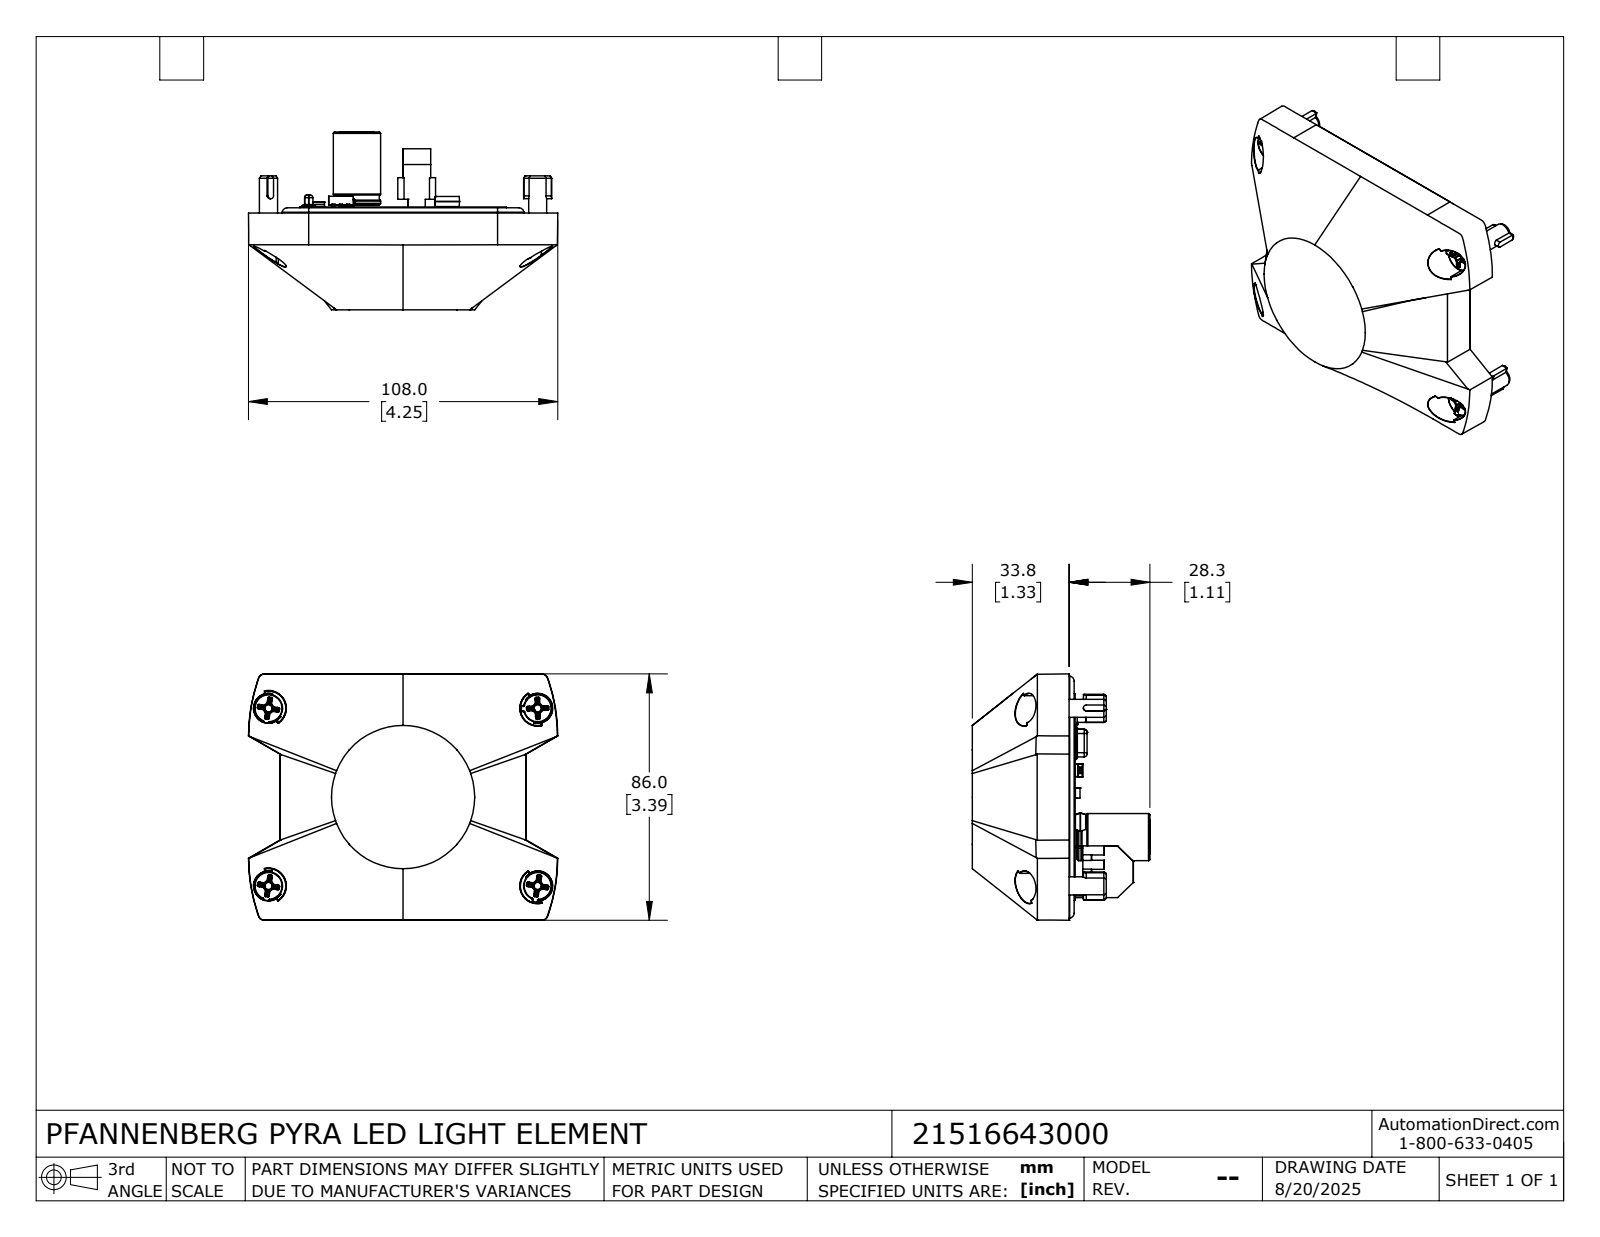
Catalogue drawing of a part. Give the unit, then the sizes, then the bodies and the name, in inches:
Units: inches
Overall size (bounding box): 4.252 × 3.386 × 2.444
Round holes (diameter × count): ⌀0.039 ×12, ⌀0.031 ×8, ⌀0.043 ×7, ⌀0.035 ×2, ⌀0.055 ×2, ⌀0.059 ×2, ⌀0.098 ×2, ⌀0.118 ×2, ⌀0.04 ×1, ⌀0.097 ×1, ⌀0.137 ×1, ⌀0.162 ×1
Round bosses / shafts (diameter × count): ⌀0.386 ×4, ⌀0.248 ×4, ⌀0.65 ×1
Partial cylindrical surfaces — rounded edges, fillets, slot ends (radius × count): R0.008 ×111, R0.004 ×8, R0.039 ×8, R0.063 ×8, R0.02 ×5, R0.057 ×4, R0.069 ×4, R0.072 ×4
Main face-to-face distances: 0.064, 0.138, 0.202, 1.414, 1.35, 1.213, 3.219, 3.189, 0.03, 0.02
Hole centre spacings: 0.2, 0.591, 1.494, 1.881, 0.188, 0.197, 0.394, 0.4
Volume: 13.38 in³ · Surface area: 82.51 in²
Bodies: 17 solids, 1949 faces (787 planar, 409 cylindrical, 753 other)
Part name (STEP PRODUCT): 21516643000
STEP written by: SolidWorks 2024 (CONFIG_CONTROL_DESIGN)
